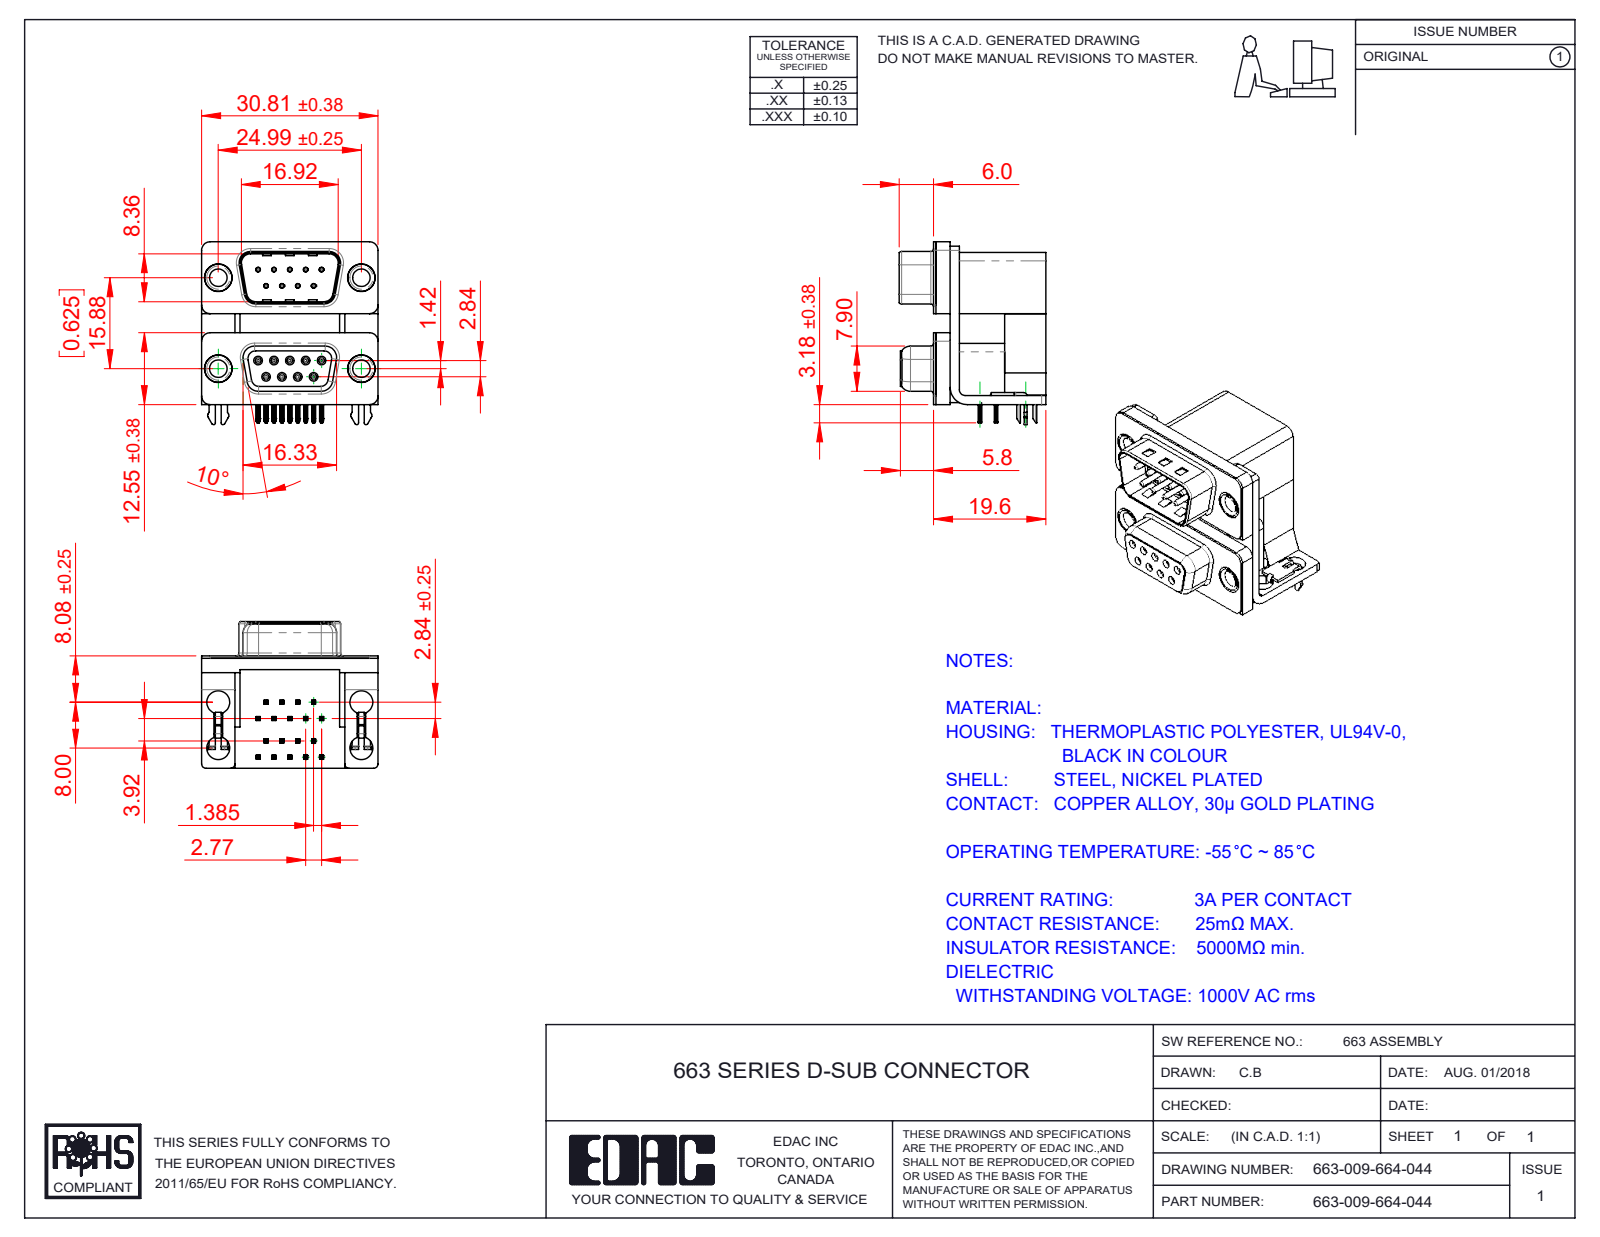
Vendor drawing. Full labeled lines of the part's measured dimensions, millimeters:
Part name (STEP PRODUCT): 663 Housing Spacer_09 Contacts L; 663 Thru Hole Rivet; 663 Contact Bottom Lower; 663 Contact Bottom Upper_L (+8 more)
STEP written by: SolidWorks 2020 (CONFIG_CONTROL_DESIGN)
Units: millimetres
Bodies: 31 solids, 2553 faces (1341 planar, 689 cylindrical, 523 other)
Overall size (bounding box): 31.93 × 30.81 × 25.6
Volume: 10 328 mm³ · Surface area: 12 181 mm²
Round holes (diameter × count): ⌀0.8 ×18, ⌀0.35 ×9, ⌀0.9 ×9, ⌀4 ×8, ⌀3.05 ×4, ⌀3.5 ×4, ⌀4.8 ×4, ⌀5 ×4
Round bosses / shafts (diameter × count): ⌀1.2 ×9, ⌀0.75 ×9, ⌀4.9 ×4, ⌀4.75 ×4, ⌀3.85 ×4
Partial cylindrical surfaces — rounded edges, fillets, slot ends (radius × count): R0.1 ×73, R0.25 ×42, R0.15 ×36, R0.12 ×18, R0.35 ×18, R0.5 ×16, R1.5 ×13, R0.75 ×10
Main face-to-face distances: 0.4, 2.5, 16.7, 19.2, 19.6, 2.9, 7.2, 9.5, 12, 12.4
Hole centre spacings: 3.16, 2.77, 16.12, 15.88, 5.54, 16.82, 13.11, 18.77
